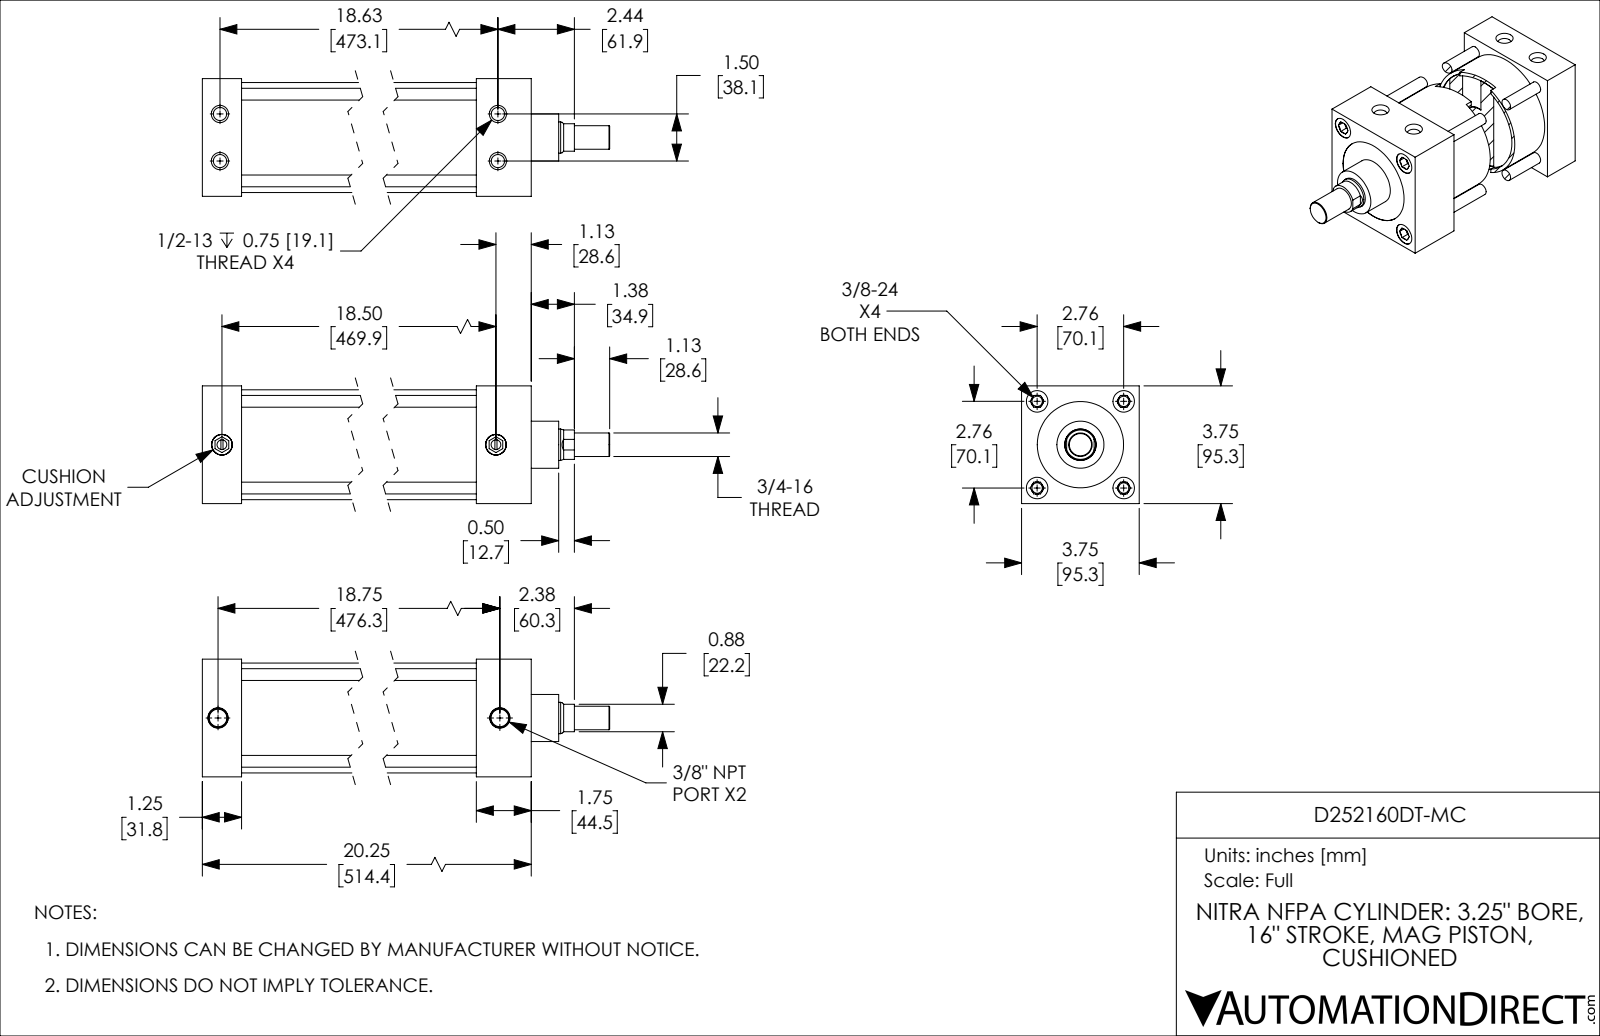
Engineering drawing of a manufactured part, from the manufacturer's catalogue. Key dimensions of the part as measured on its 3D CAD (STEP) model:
Part name (STEP PRODUCT): D252160DT-MC; D252160DT-MC_PISTON_KK1; D252160DT-MC_BODY; D252160DT-MC_CUSHION
STEP written by: SolidWorks 2019 (CONFIG_CONTROL_DESIGN)
Units: inches
Bodies: 4 solids, 246 faces (90 planar, 78 cylindrical, 78 other)
Overall size (bounding box): 22.75 × 3.75 × 3.75
Volume: 95.63 in³ · Surface area: 670.7 in²
Round holes (diameter × count): ⌀0.332 ×4, ⌀0.422 ×4, ⌀0.687 ×4, ⌀0.312 ×2, ⌀0.562 ×2, ⌀0.656 ×2, ⌀1.001 ×1, ⌀2.75 ×1, ⌀3.251 ×1
Round bosses / shafts (diameter × count): ⌀0.375 ×4, ⌀0.657 ×2, ⌀3.501 ×1, ⌀3.249 ×1, ⌀1.5 ×1, ⌀0.999 ×1, ⌀0.75 ×1
Partial cylindrical surfaces — rounded edges, fillets, slot ends (radius × count): R0.469 ×1
Main face-to-face distances: 1.25, 3.75, 18.5, 17.25, 2.5, 16, 20.25, 19, 17.75, 1.75
Hole centre spacings: 0.753, 1.952, 2.76, 18.702, 1.5, 3.903, 18.625, 18.685
